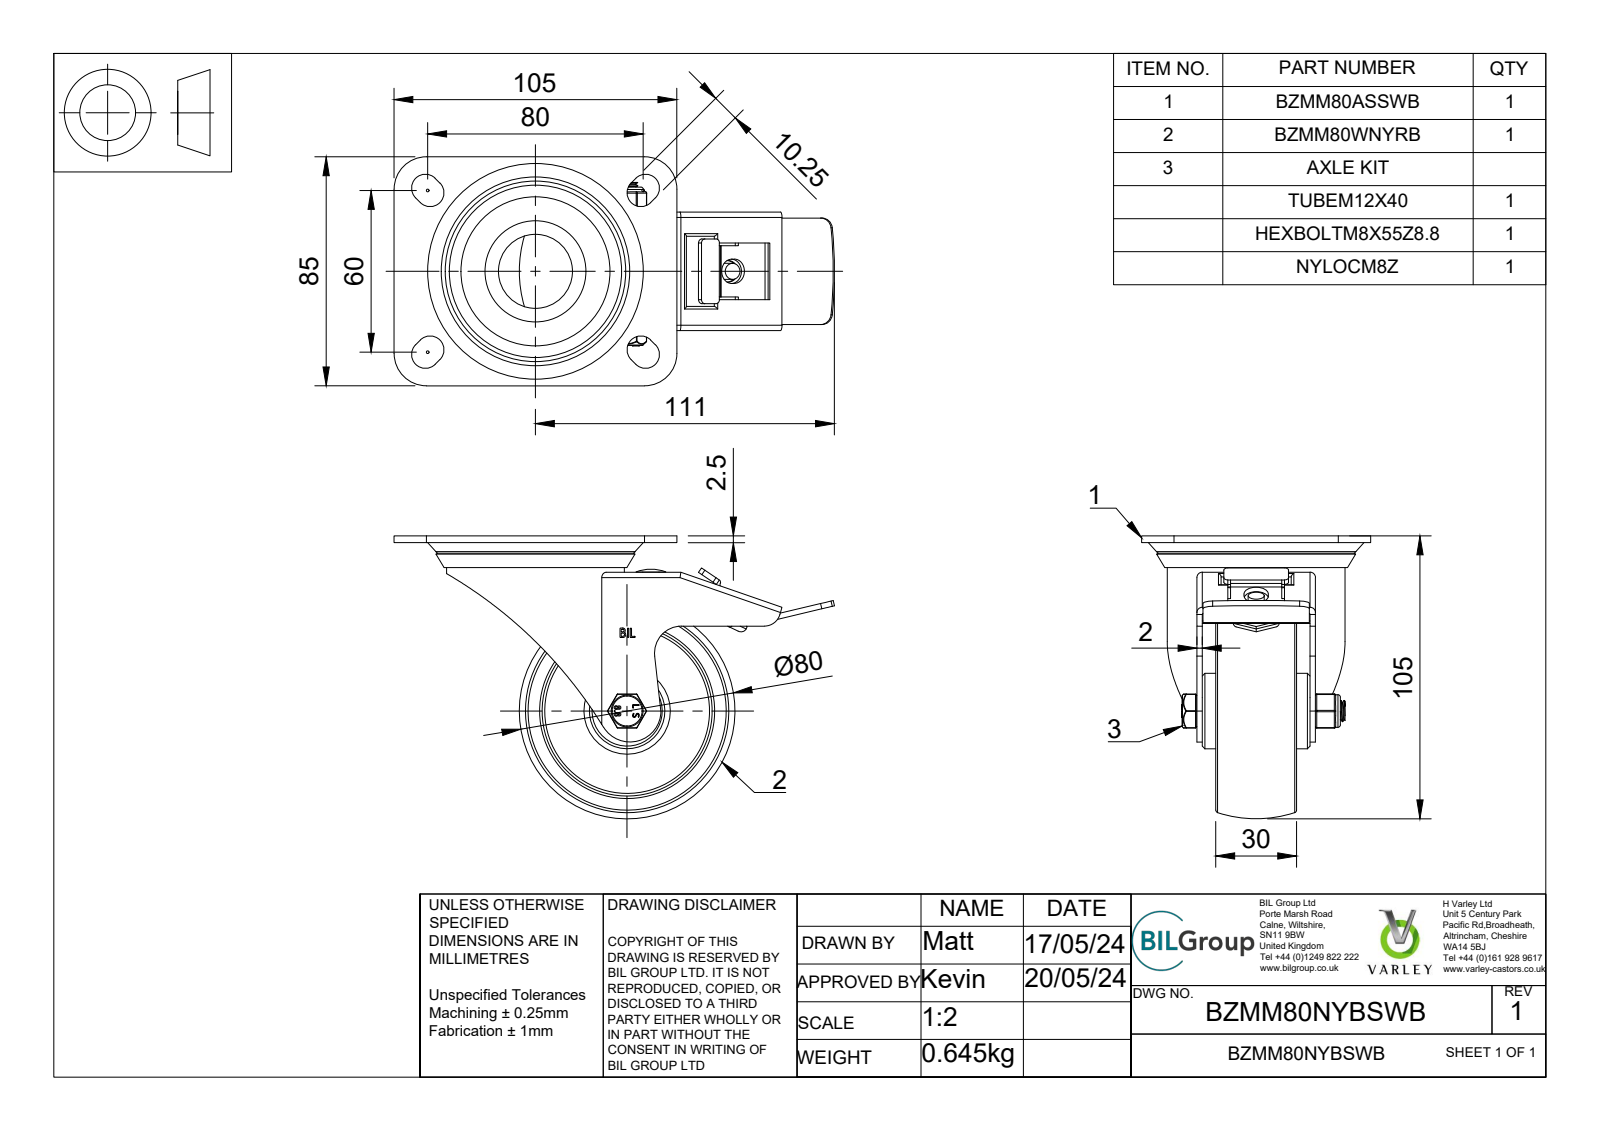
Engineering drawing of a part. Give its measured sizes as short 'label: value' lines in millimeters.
name: BZMM80NYBSWB v4; BZMM80ASSWB v1; ZINC PLATED, PRESSED STEEL TOP PLATE; ZINC PLATED, PRESSED STEEL TOP PLATE Geometry (+7 more)
written by: Autodesk Translation Framework v13.14.0.145 (AUTOMOTIVE_DESIGN)
unit: mm
bodies: 47 solids, 707 faces (361 planar, 226 cylindrical, 120 other)
size: 163.5 × 105 × 85
volume: 147 984 mm³; area: 102 318 mm²
holes: 2× ⌀0.66, 2× ⌀8, 1× ⌀6, 1× ⌀8.2, 1× ⌀8.4, 1× ⌀8.6, 1× ⌀12.4, 1× ⌀12.5, 1× ⌀23, 1× ⌀27.5, 1× ⌀56, 1× ⌀62
bosses: 8× ⌀3.75, 1× ⌀66, 1× ⌀31.5, 1× ⌀28, 1× ⌀19.5, 1× ⌀12.1, 1× ⌀11.9, 1× ⌀11.5
rounds: 24× R0.5, 14× R1, 12× R0.25, 11× R2, 8× R5.12, 4× R0.33, 4× R0.64, 4× R1.5
face distances: 2, 2.5, 18, 13, 22, 20, 5, 24, 42, 4
hole spacings: 3.22, 2.49, 42.86
